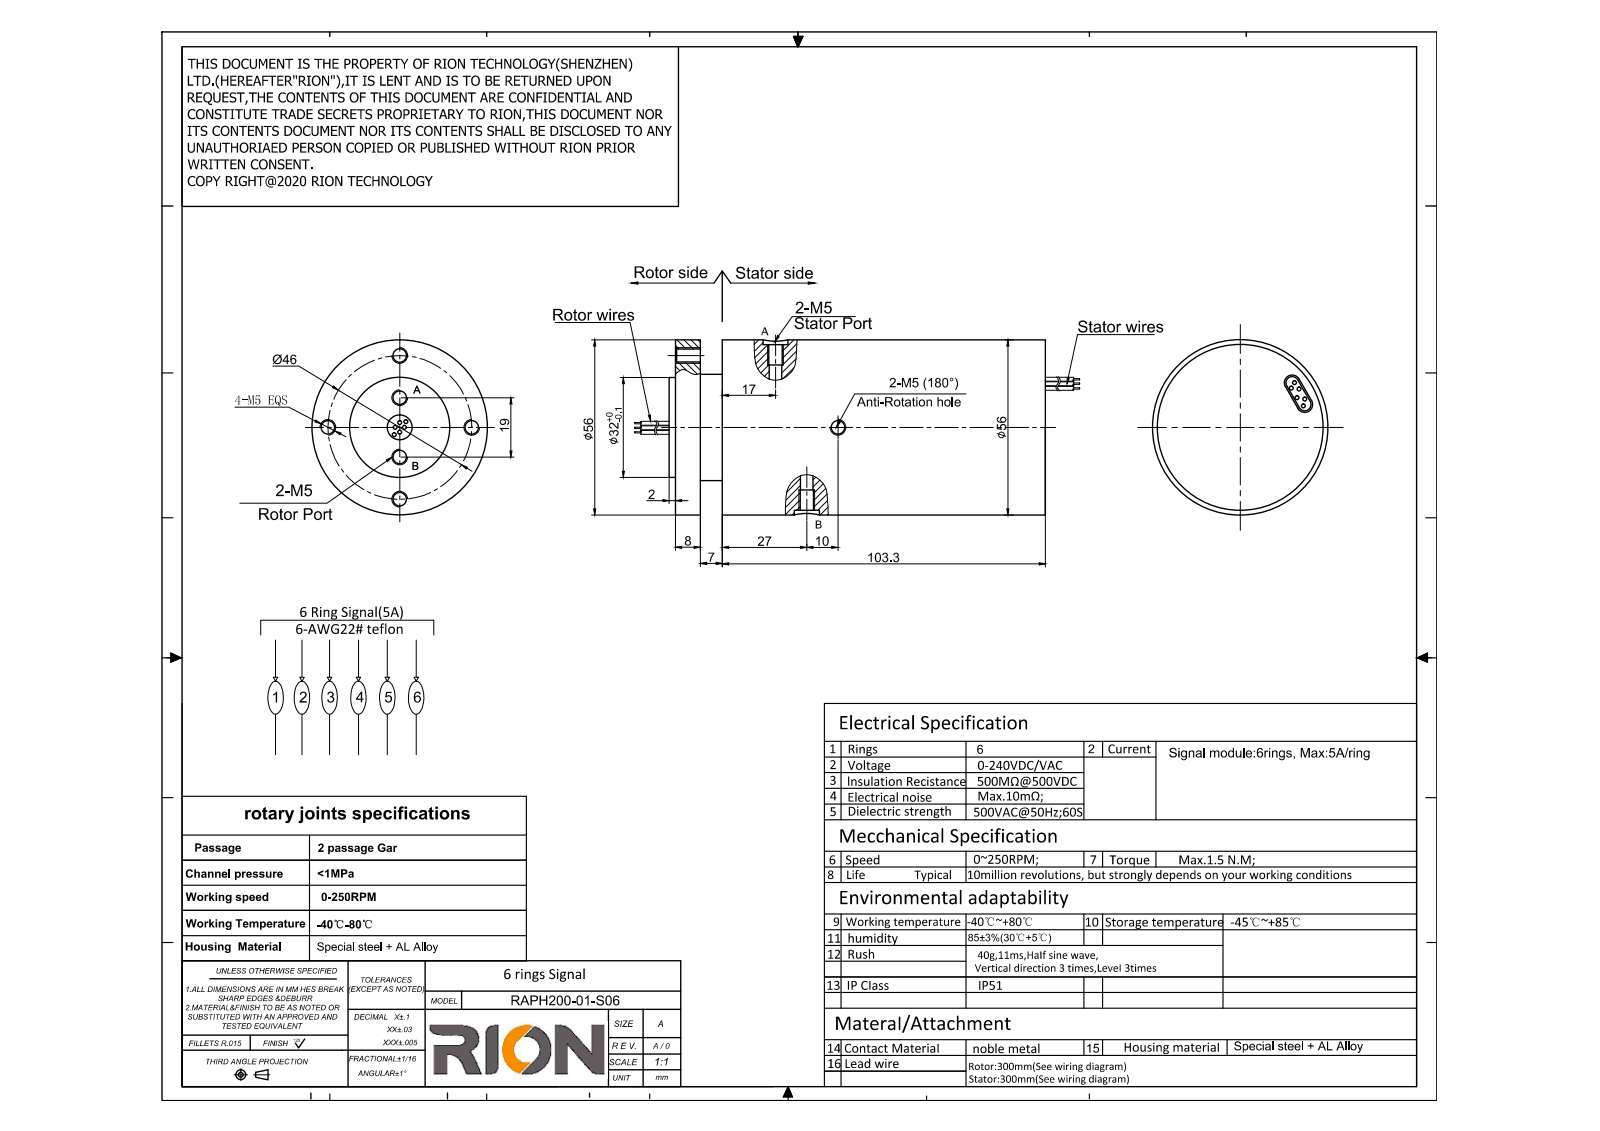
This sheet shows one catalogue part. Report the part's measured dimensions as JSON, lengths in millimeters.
{"part_name": "RAPH200-01-S06", "step_written_by": "SolidWorks 2014 (CONFIG_CONTROL_DESIGN)", "units": "millimeters", "bodies": {"solids": 1, "faces": 114, "planar": 27, "cylindrical": 75, "other": 12}, "overall_size": [143.3, 56, 56], "volume_mm3": 280364, "surface_area_mm2": 32589, "round_holes": [[4.2, 9], [3, 4], [8, 2], [11, 1], [53, 1]], "round_bosses_or_shafts": [[1.4, 6], [1.3, 6], [56, 1], [52.8, 1], [34, 1], [32, 1]], "partial_cylinders_radius": [[2.5, 2]], "face_to_face_distances": [118.3, 15, 103.3, 8, 7, 110.3, 10, 2, 17, 120.3], "hole_center_spacings": [23, 24.88, 32.53, 9.5, 13.5, 32.5, 46, 10]}
